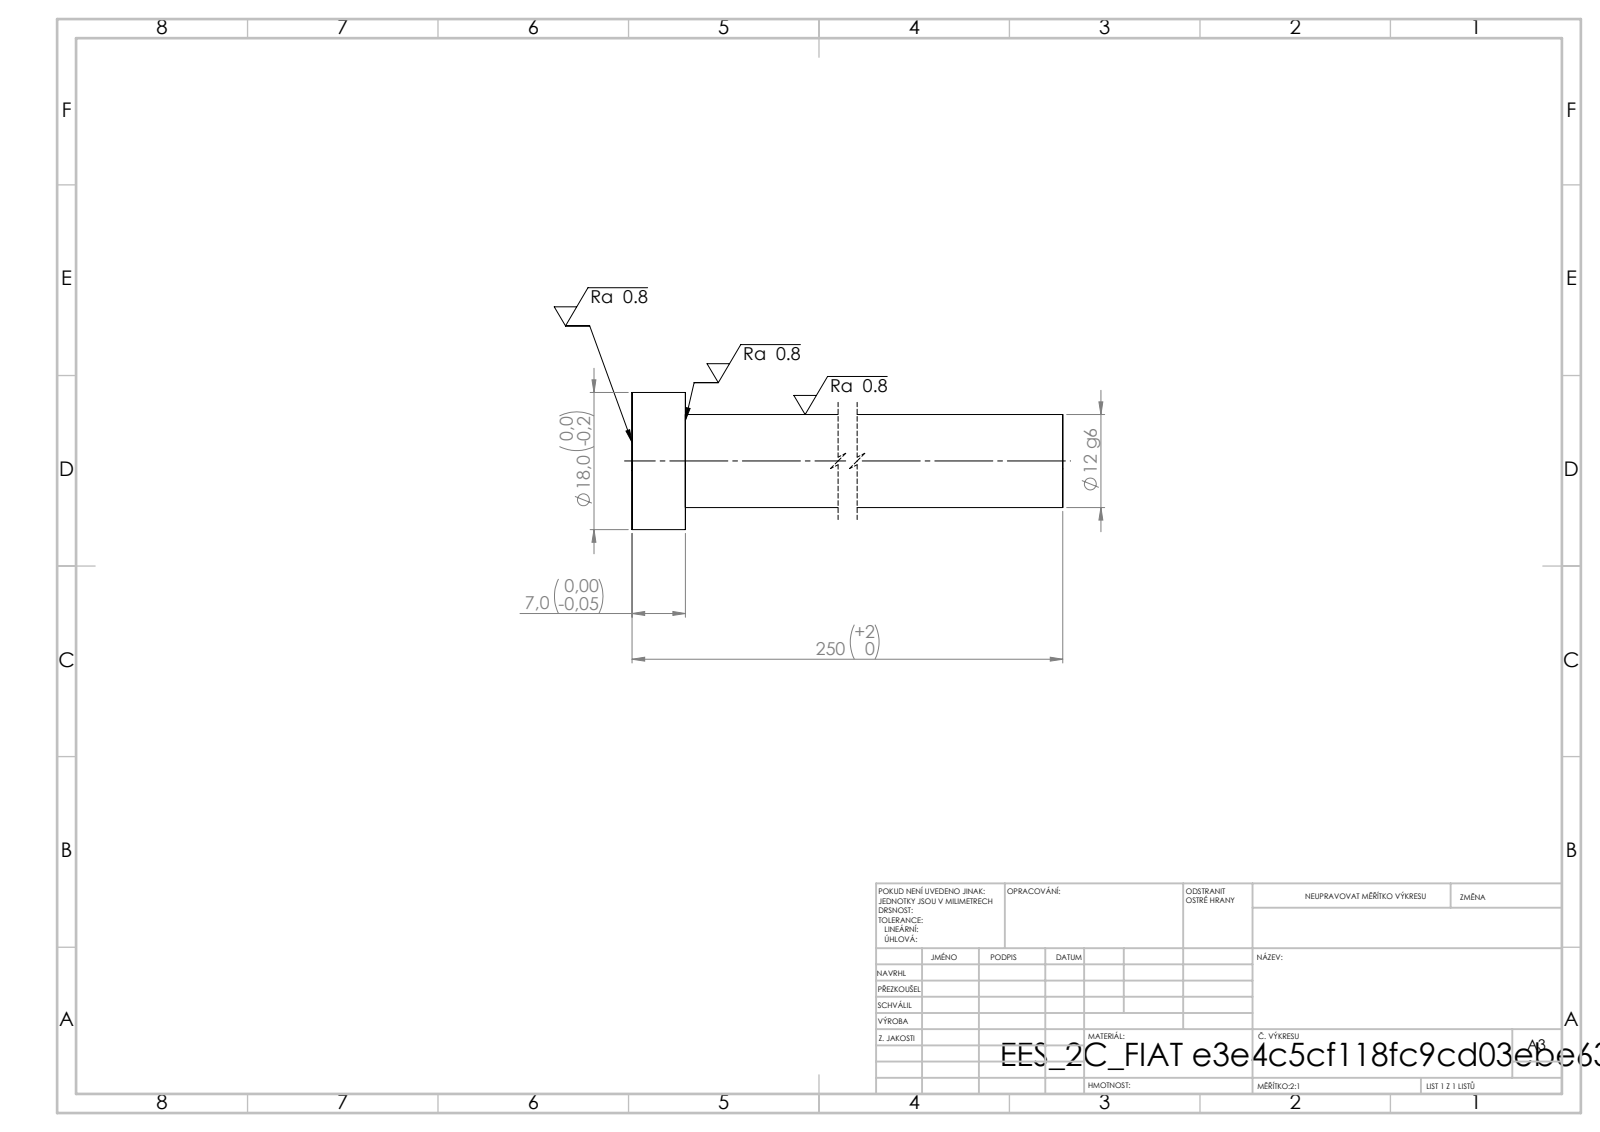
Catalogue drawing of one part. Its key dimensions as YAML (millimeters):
step_written_by: "SolidWorks 2019 (CONFIG_CONTROL_DESIGN)"
units: millimeters
bodies: {solids: 1, faces: 7, planar: 3, cylindrical: 4, other: 0}
overall_size: [250, 18, 18]
volume: 30188
surface_area: 10218
round_bosses_or_shafts:
  - {diameter: 18, count: 1}
  - {diameter: 12.2, count: 1}
face_to_face_distances: [7, 250, 243]
